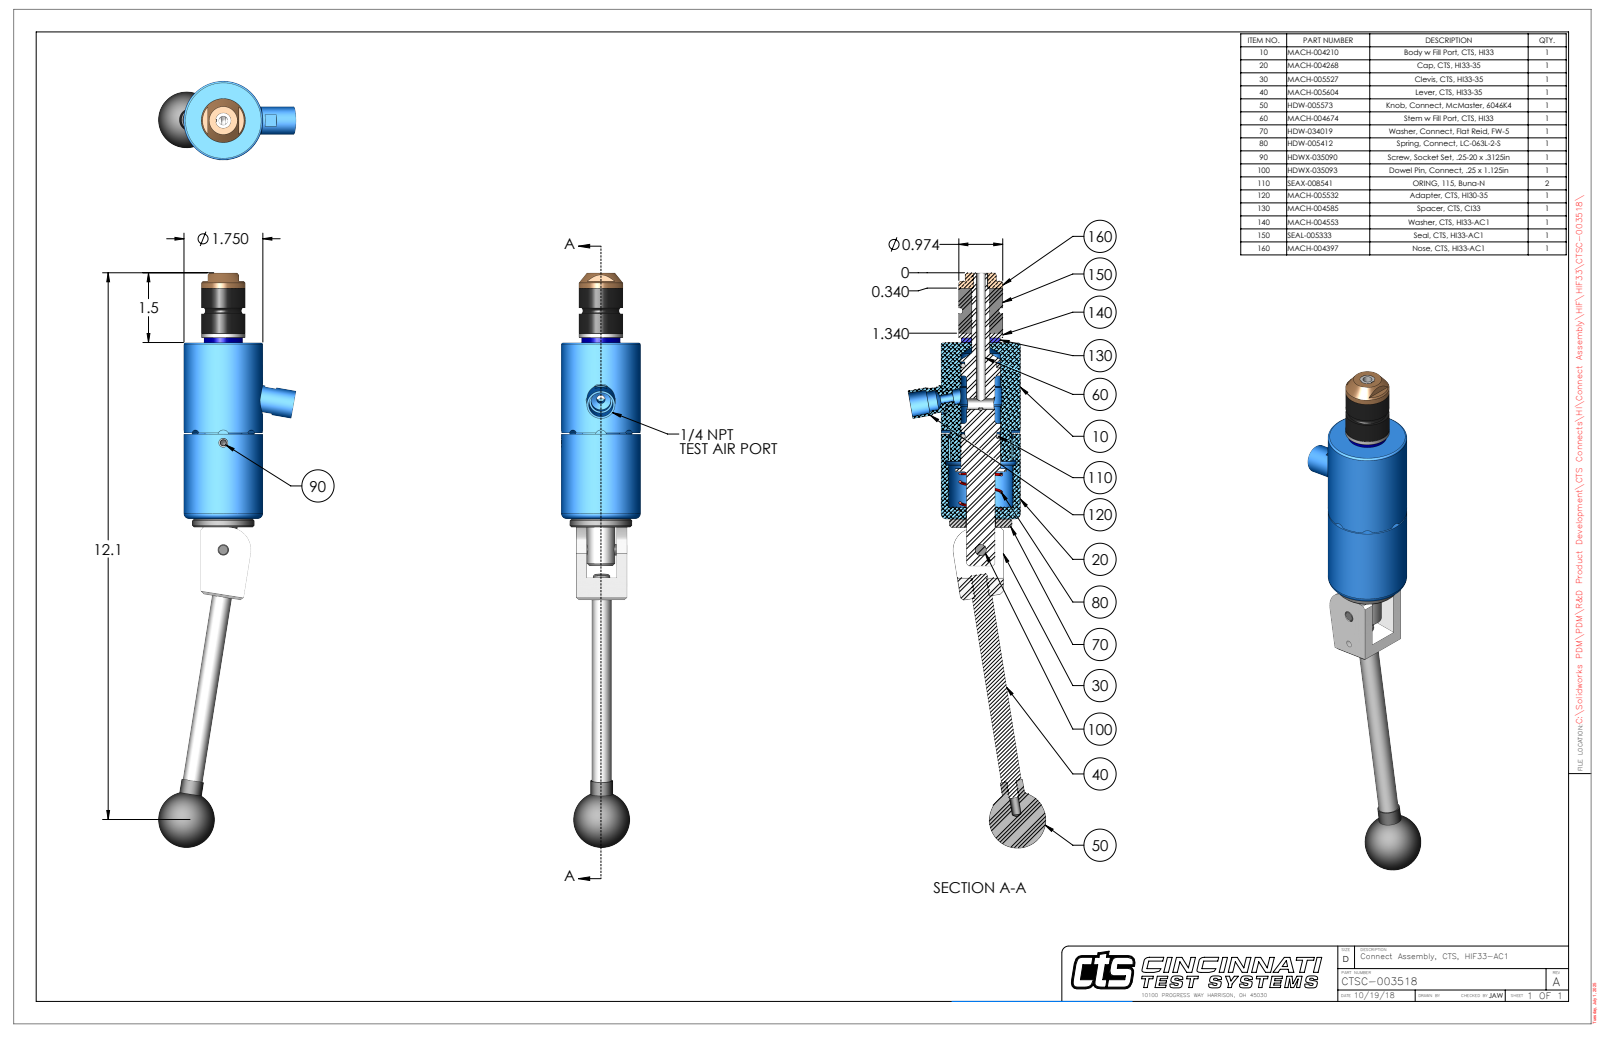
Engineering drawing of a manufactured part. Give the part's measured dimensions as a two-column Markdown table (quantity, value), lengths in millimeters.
| quantity | value |
| --- | --- |
| part name | CTSC-003518 |
| STEP written by | SolidWorks 2023 (AUTOMOTIVE_DESIGN) |
| units | millimeters |
| bodies | 10 solids, 275 faces (89 planar, 121 cylindrical, 65 other) |
| overall size | 323.9 × 77.3 × 44.5 |
| volume | 223 000 mm³ |
| surface area | 48 550 mm² |
| round holes (diameter × count) | 5.1 × 2, 8 × 2, 3.8 × 1, 4.7 × 1, 5.2 × 1, 6.3 × 1, 6.4 × 1, 6.4 × 1, 9.9 × 1, 10.1 × 1, 10.2 × 1, 11.1 × 1 |
| round bosses / shafts (diameter × count) | 9.5 × 2, 7.9 × 2, 6.4 × 2, 44.5 × 1, 35.1 × 1, 24.7 × 1, 21.8 × 1, 15.9 × 1 |
| partial cylindrical surfaces (radius × count) | 3.2 × 4, 0.7 × 2, 3.7 × 1, 8.4 × 1, 12.7 × 1, 17.7 × 1, 21.4 × 1 |
| main face-to-face distances | 99.2, 28.4, 30.7, 129.9, 134.7, 104, 4.8, 25.4, 5.3, 104.5 |
| hole center spacings | 18.8, 60.4, 79.1 |
